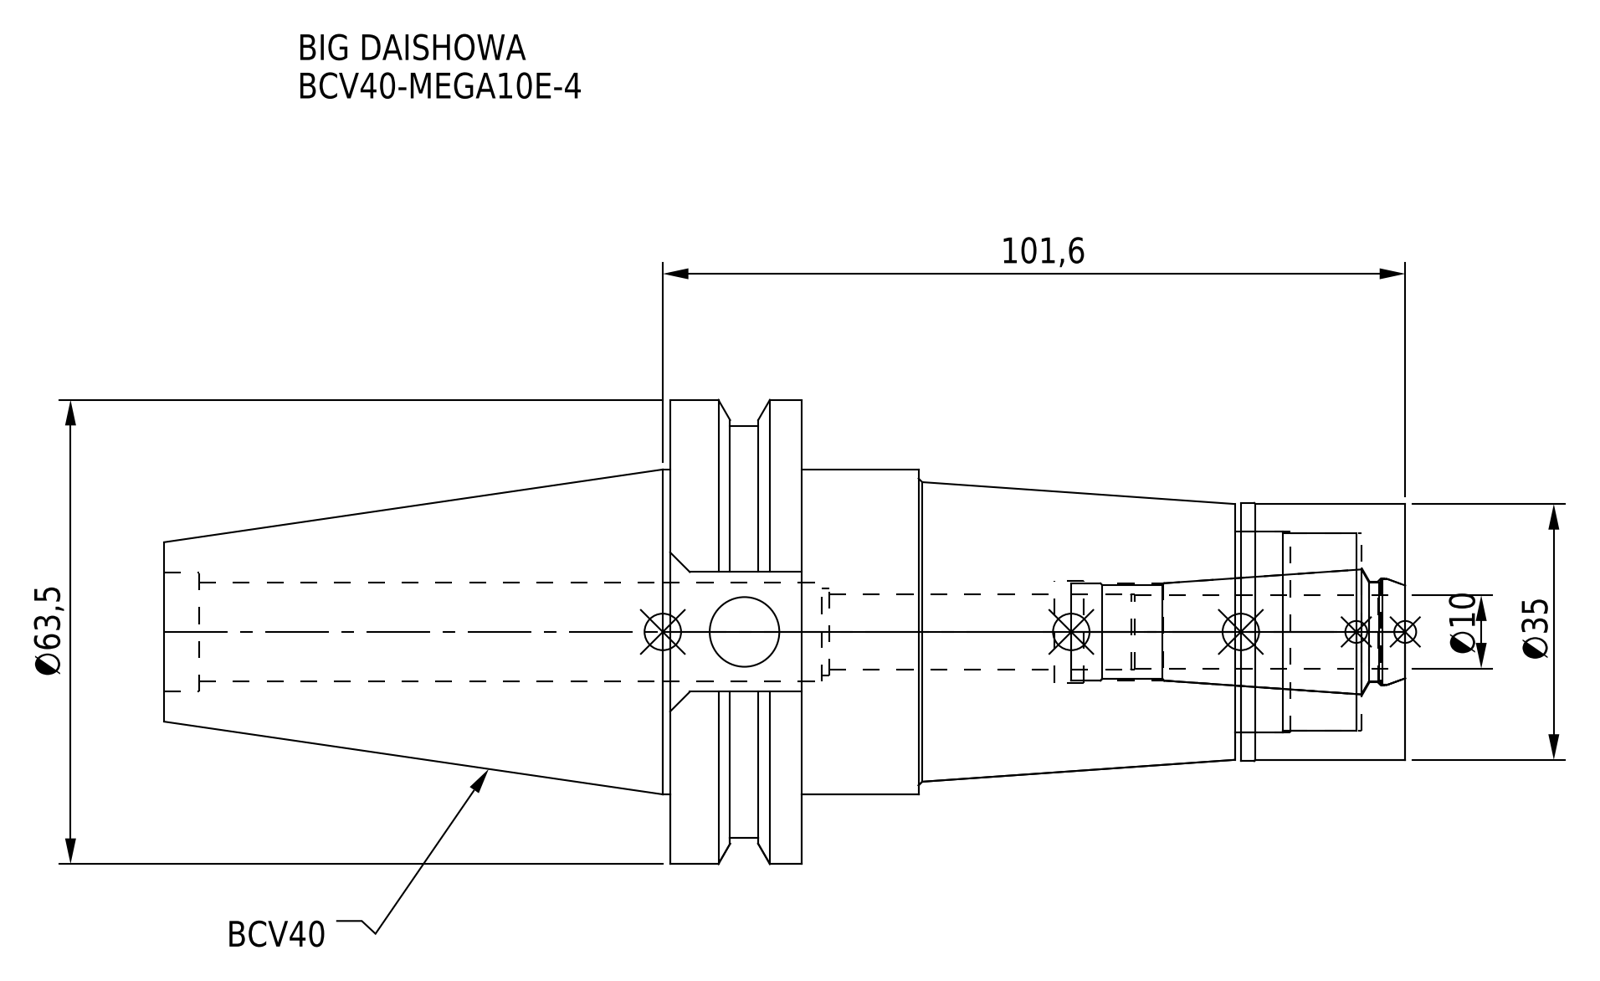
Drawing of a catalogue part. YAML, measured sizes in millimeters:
part_name: "BCV40ME10040-010_ASM.stp; BCV40-MEGA10E-4; DXF_TEMP_ASSY_ASM_4_ASM.stp; BCV40-MEGA10E-4-100.stp (+3 more)"
step_written_by: "SolidWorks 2019 (CONFIG_CONTROL_DESIGN)"
units: millimeters
bodies: {solids: 2, faces: 93, planar: 31, cylindrical: 42, other: 20}
overall_size: [169.85, 63.5, 61.35]
volume: 188610
surface_area: 37803
round_holes:
  - {diameter: 9.53, count: 1}
  - {diameter: 10.4, count: 1}
  - {diameter: 12, count: 1}
  - {diameter: 13.3, count: 1}
  - {diameter: 13.6, count: 1}
  - {diameter: 13.8, count: 1}
  - {diameter: 13.9, count: 1}
  - {diameter: 14.7, count: 1}
  - {diameter: 16.32, count: 1}
  - {diameter: 27, count: 1}
  - {diameter: 27.5, count: 1}
round_bosses_or_shafts:
  - {diameter: 63.5, count: 1}
  - {diameter: 56.36, count: 1}
  - {diameter: 44.45, count: 1}
  - {diameter: 35.3, count: 1}
  - {diameter: 35, count: 1}
face_to_face_distances: [18.05, 82.55, 100.6, 6, 22.5, 60.05, 78.1, 23.3, 0.8, 59.25]
